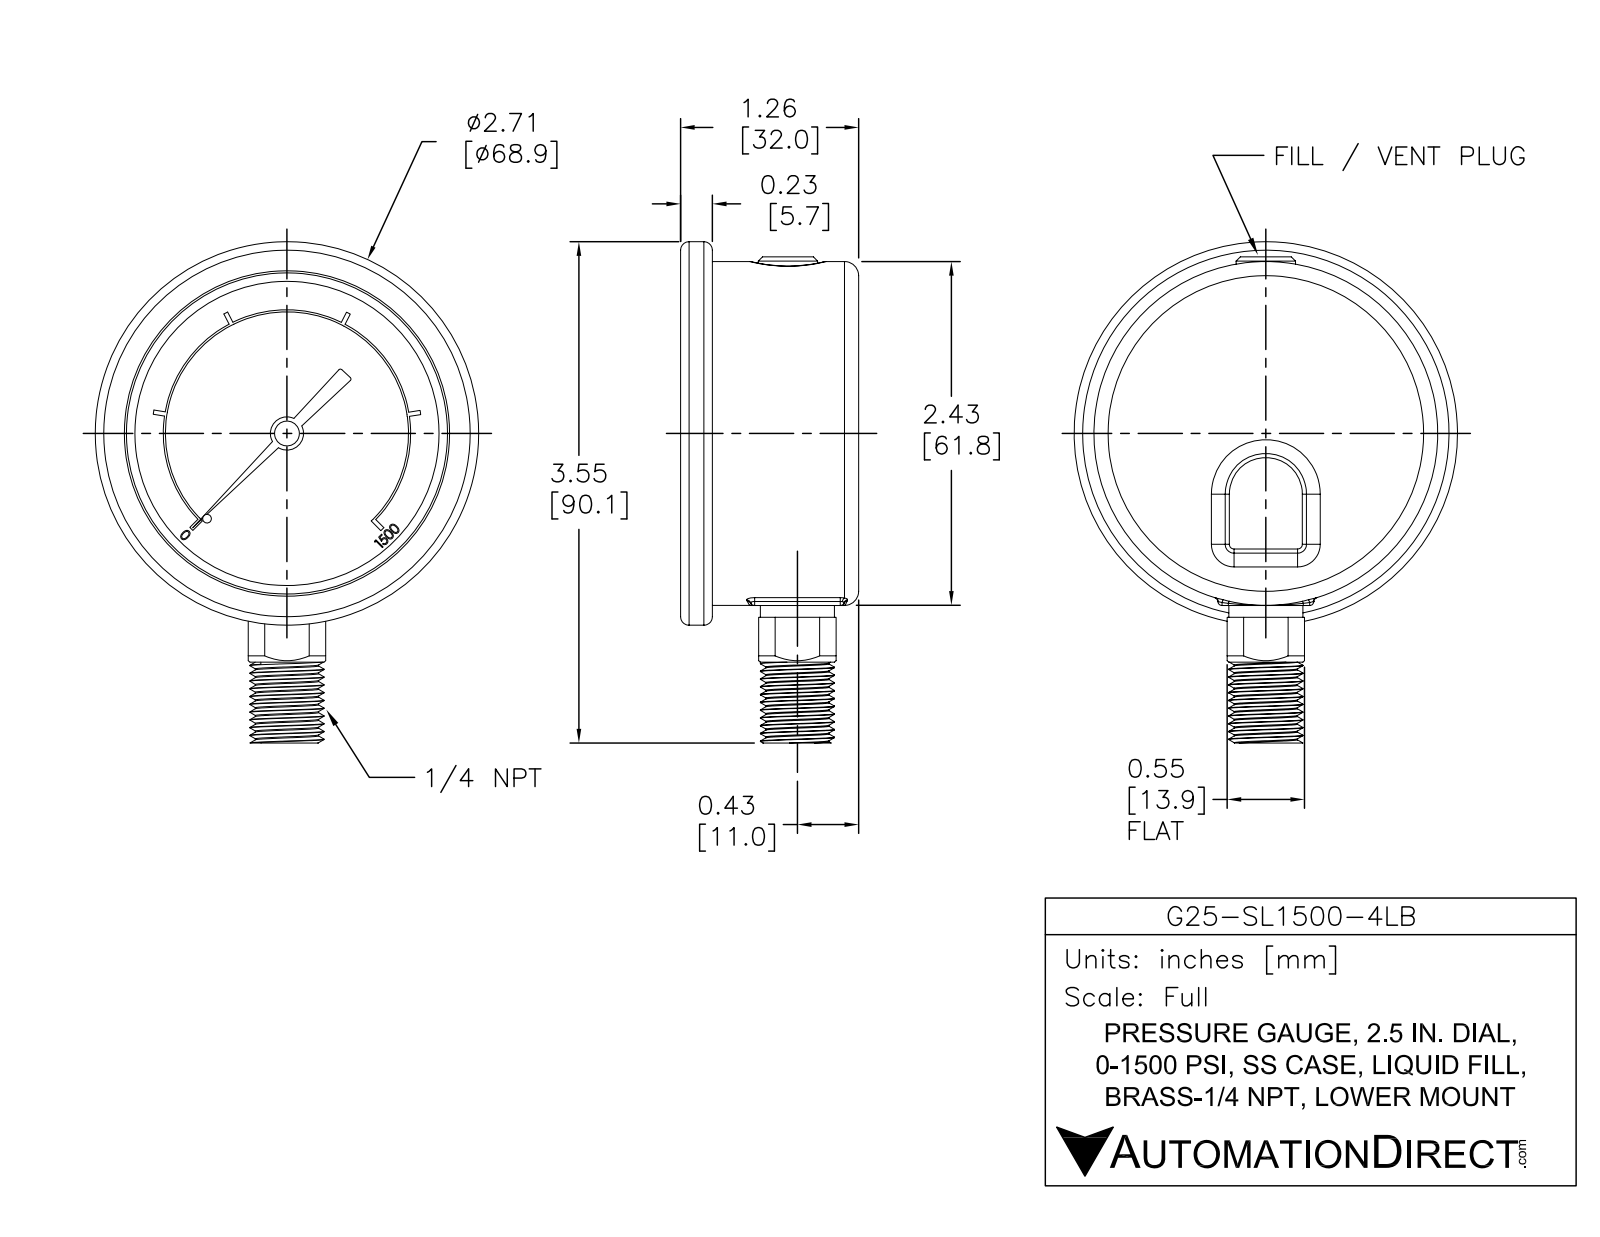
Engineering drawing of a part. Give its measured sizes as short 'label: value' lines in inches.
name: G25-SL1500-4LB
written by: SolidWorks 2021 (AUTOMOTIVE_DESIGN)
unit: in
bodies: 1 solid, 358 faces (202 planar, 85 cylindrical, 71 other)
size: 3.546 × 2.713 × 1.26
volume: 5.273 in³; area: 24.68 in²
holes: 1× ⌀0.027, 1× ⌀0.071, 1× ⌀0.119, 1× ⌀2.272
bosses: 1× ⌀2.713, 1× ⌀2.433, 1× ⌀0.524, 1× ⌀0.42, 1× ⌀0.235, 1× ⌀0.176, 1× ⌀0.14, 1× ⌀0.041
rounds: 9× R0.03, 3× R0.1, 2× R0.015, 1× R0.316, 1× R0.86, 1× R0.875
face distances: 1.01, 1.26, 0.25, 1.035, 0.025, 0.225, 0.1, 0.91, 0.935, 1.16
hole spacings: 0.067
